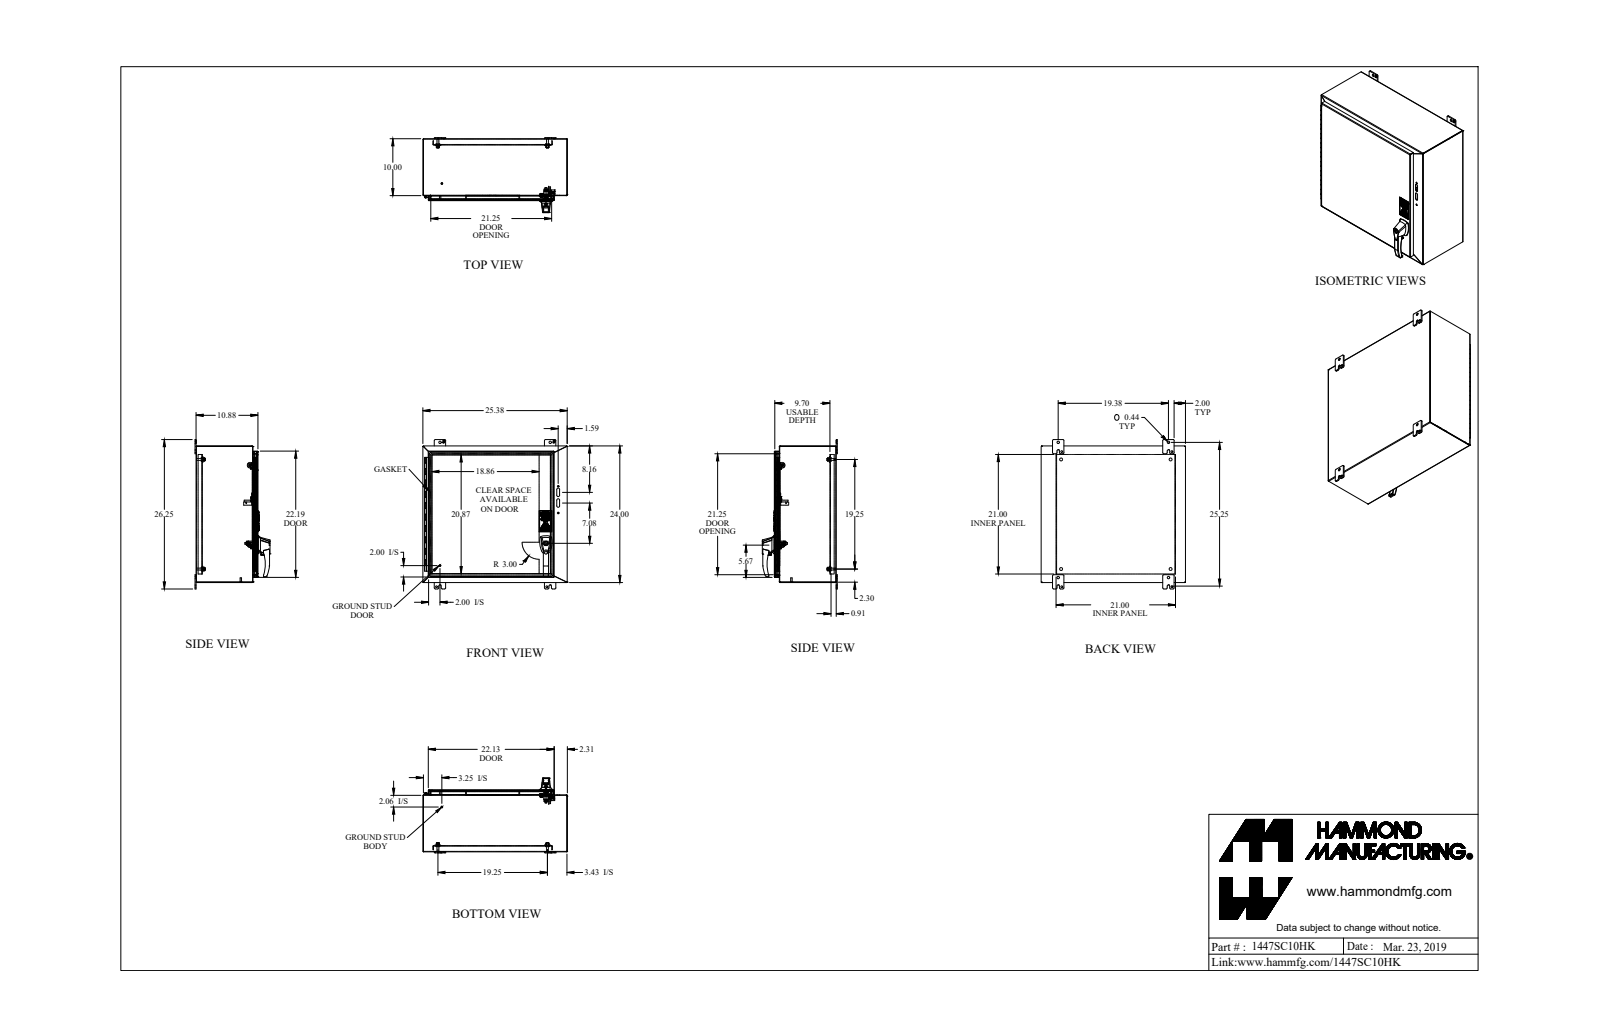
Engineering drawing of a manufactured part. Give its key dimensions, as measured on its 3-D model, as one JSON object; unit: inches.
{"part_name": "1447SC10HK", "step_written_by": "SolidWorks 2019 (AUTOMOTIVE_DESIGN)", "units": "inches", "bodies": {"solids": 49, "faces": 1157, "planar": 711, "cylindrical": 331, "other": 115}, "overall_size": [26.25, 25.375, 13.177], "volume_in3": 244.5, "surface_area_in2": 6140, "round_holes": [[0.313, 5], [0.176, 4], [0.437, 4], [0.5, 4], [0.156, 2], [0.173, 2], [0.215, 2], [0.25, 2], [0.265, 2], [0.281, 2], [0.307, 2], [0.413, 2]], "round_bosses_or_shafts": [[0.375, 8], [0.25, 7], [1, 4], [0.65, 4], [0.33, 4], [0.156, 4], [0.5, 2], [0.402, 2]], "partial_cylinders_radius": [[0.079, 28], [0.187, 24], [0.007, 16], [0.25, 12], [0.125, 11], [0.03, 8], [0.151, 8], [0.218, 8]], "face_to_face_distances": [0.072, 10.803, 10.731, 23.928, 10.875, 25.303, 0.095, 9.771, 9.699, 1.032], "hole_center_spacings": [19.25, 19.375, 1.111, 1.735, 1.736, 1.855, 6.754, 13.969]}
